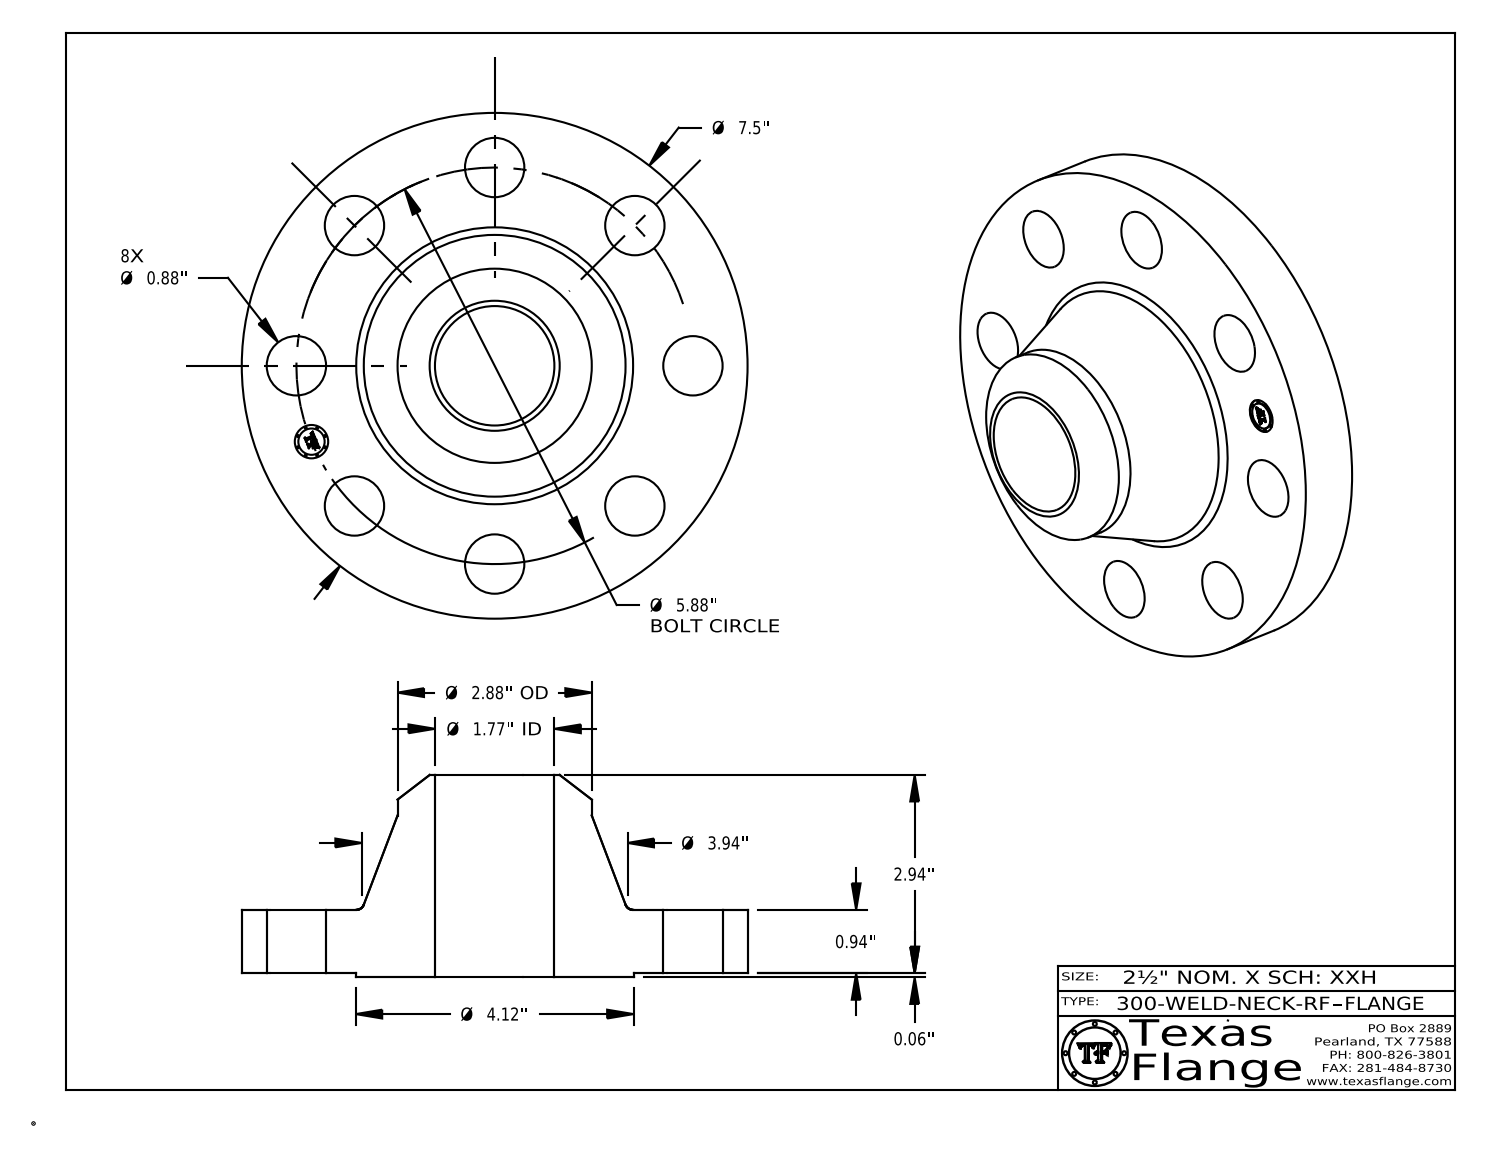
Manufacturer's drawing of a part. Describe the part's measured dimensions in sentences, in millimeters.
The part is named "300-WELD-NECK-RF". Its 3-D file was written by "CATIA V5 STEP AP214 (AUTOMOTIVE_DESIGN)". It is 1 solid with 419 faces: 369 planar, 44 cylindrical and 6 other. Overall it measures 190.5 by 190.5 by 76.3 millimeters. Its volume is 762 000 cubic millimeters and its surface area 95 100 square millimeters. Round holes: 8 of diameter 22.4, 1 of diameter 12.6, 1 of diameter 45. Round bosses or shafts: 8 of diameter 0.8, 1 of diameter 190.5, 1 of diameter 104.6, 1 of diameter 73.2, 1 of diameter 9.9. The main face-to-face distances are 23.9, 1.6, 25.5, 76.3, 74.7, 50.8, 0.4, 25.1, 23.5, 51.2. The hole center spacings are 57.2, 138, 74.7, 74.7, 105.6, 105.6, 83, 149.4.
